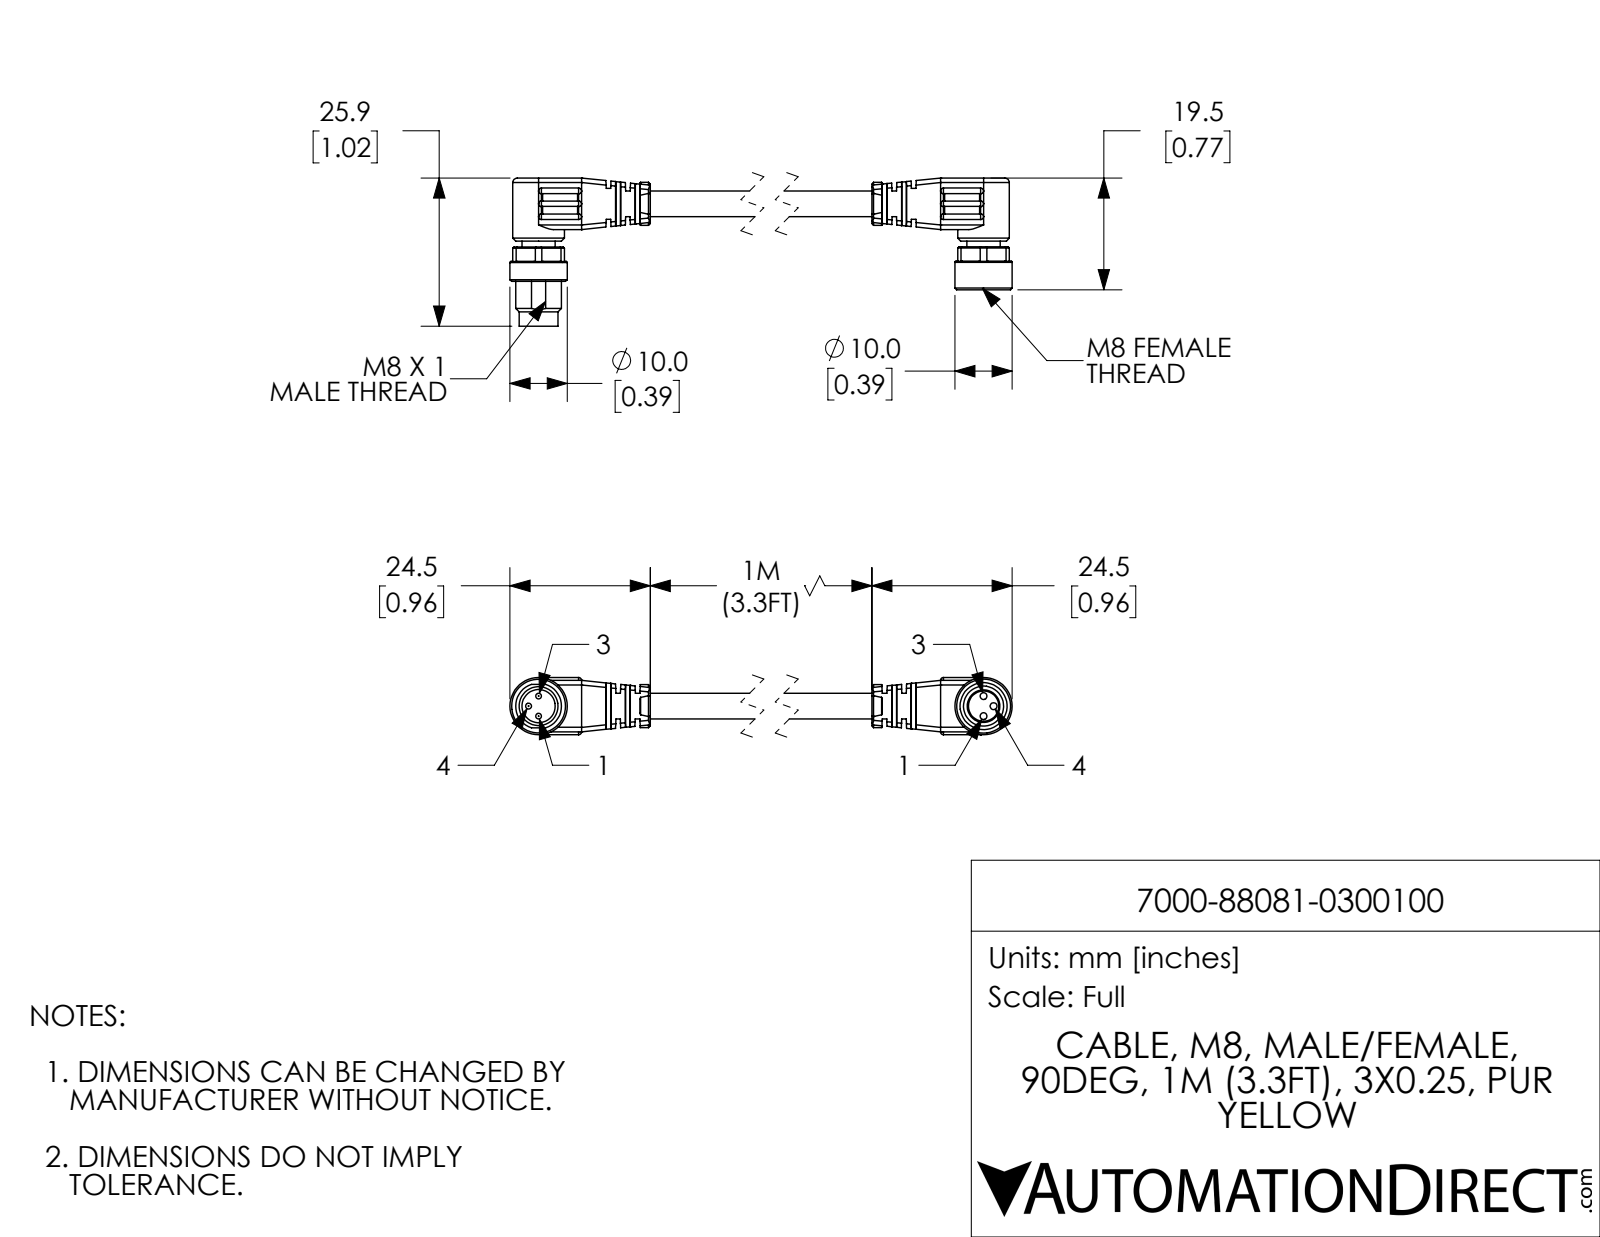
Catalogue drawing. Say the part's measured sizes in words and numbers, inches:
The part is named "7000-88081-0300100_MALE; 7000-88081-0300100; 7000-88081-0300100_FEMALE". Its 3-D file was written by "SolidWorks 2021 (CONFIG_CONTROL_DESIGN)". It is 2 solids with 410 faces: 190 planar, 144 cylindrical and 76 other. Overall it measures 3.976 by 1.018 by 0.394 inches. Its volume is 0.317 cubic inches and its surface area 6.059 square inches. Round holes: 3 of diameter 0.047, 1 of diameter 0.228, 1 of diameter 0.276. Round bosses or shafts: 3 of diameter 0.039, 2 of diameter 0.394, 2 of diameter 0.354, 1 of diameter 0.315, 1 of diameter 0.268, 1 of diameter 0.228, 1 of diameter 0.224, 1 of diameter 0.177. Partial cylindrical surfaces (rounded edges, fillets, slot ends): 12 of radius 0.031, 8 of radius 0.008, 6 of radius 0.02, 2 of radius 0.193, 1 of radius 0.148. The main face-to-face distances are 0.041, 0.354, 0.042, 0.266, 0.362, 0.089, 0.024, 0.133, 0.472, 2.353. The hole center spacings are 0.069, 0.097, 3.583, 0.138, 3.583, 3.652.
